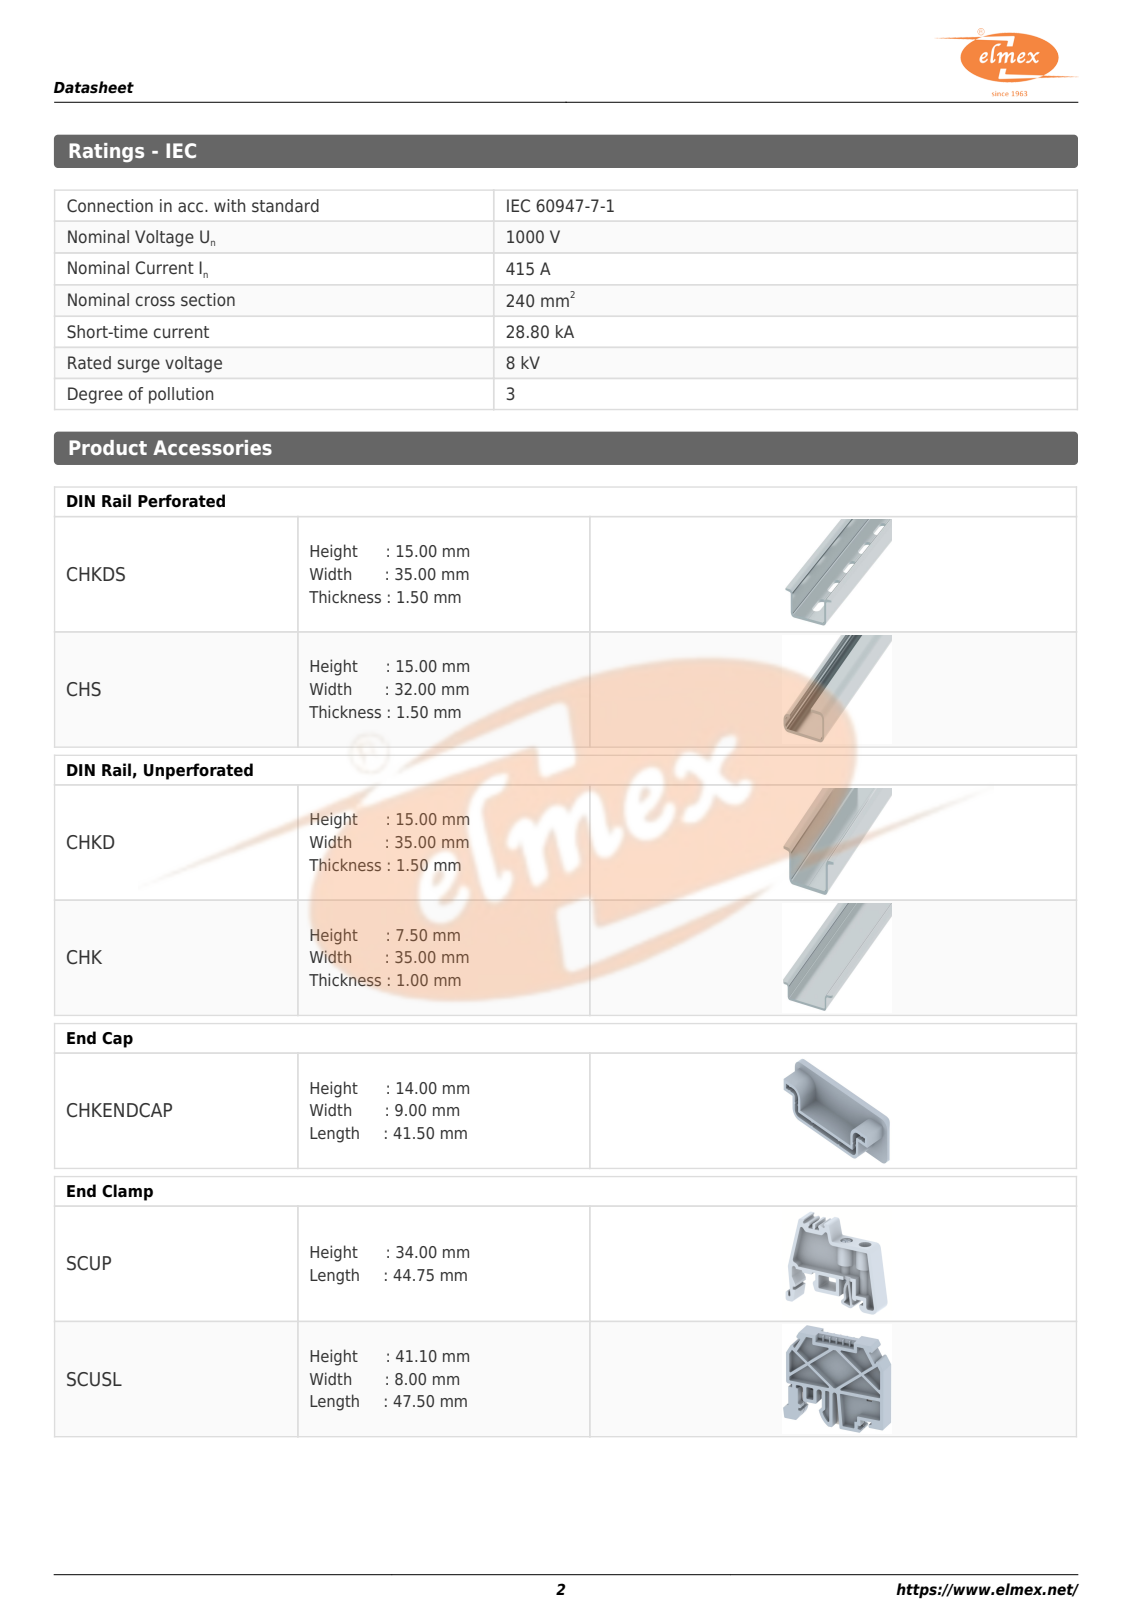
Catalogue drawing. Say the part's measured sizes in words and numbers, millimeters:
The part is named "SPT300; SPT300H; 6SPT300PC". Its 3-D file was written by "ST-DEVELOPER v16 (AUTOMOTIVE_DESIGN)". It is 4 solids with 260 faces: 198 planar, 38 cylindrical and 24 other. Overall it measures 286.8 by 89.3 by 61 millimeters. Its volume is 1 061 000 cubic millimeters and its surface area 135 850 square millimeters. Round holes: 4 of diameter 2, 2 of diameter 4.3. Round bosses or shafts: 10 of diameter 6, 6 of diameter 4. Partial cylindrical surfaces (rounded edges, fillets, slot ends): 4 of radius 0.75, 4 of radius 2, 2 of radius 0.65, 2 of radius 2.42. The main face-to-face distances are 27.5, 0.6, 54.4, 26.9, 55, 53.8, 71.5, 68.9, 2.6, 88.6. The hole center spacings are 10, 36, 55.3, 65.1, 90.78, 100.71, 26, 46.
